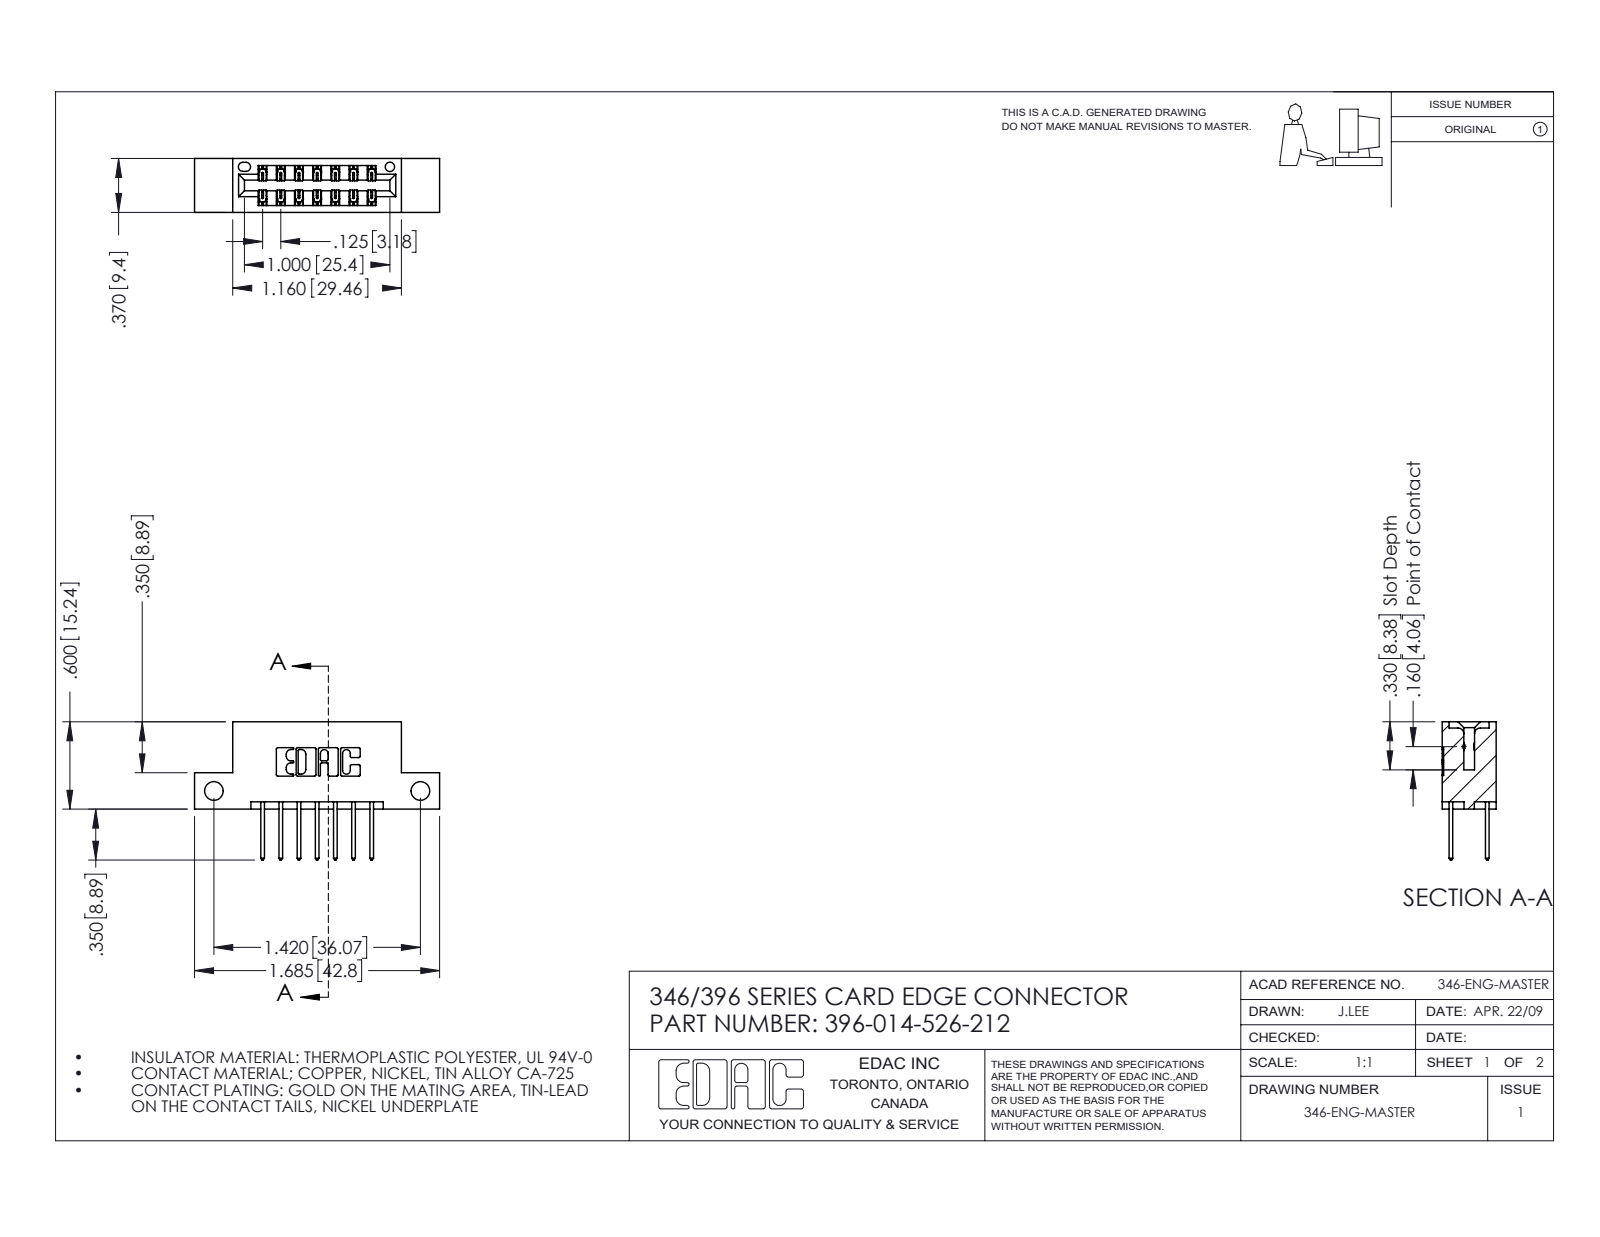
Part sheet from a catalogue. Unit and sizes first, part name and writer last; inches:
Units: inches
Overall size (bounding box): 1.685 × 0.95 × 0.37
Round holes (diameter × count): ⌀0.128 ×2, ⌀0.064 ×1
Partial cylindrical surfaces — rounded edges, fillets, slot ends (radius × count): R0.01 ×22, R0.006 ×21, R0.01 ×14, R0.007 ×6, R0.031 ×6, R0.026 ×3, R0.014 ×2, R0.022 ×2
Main face-to-face distances: 0.25, 0.048, 0.322, 0.37, 0.072, 0.298, 0.025, 0.275, 0.148, 0.222
Hole centre spacings: 1.42
Volume: 0.234 in³ · Surface area: 7.269 in²
Bodies: 15 solids, 850 faces (566 planar, 284 cylindrical, 0 other)
Part name (STEP PRODUCT): 345-292-001_345-293-126; 346 Part_Flush Mounting Lugs - Side Mount; 396-014-526-212
STEP written by: SolidWorks 2016 (CONFIG_CONTROL_DESIGN)
